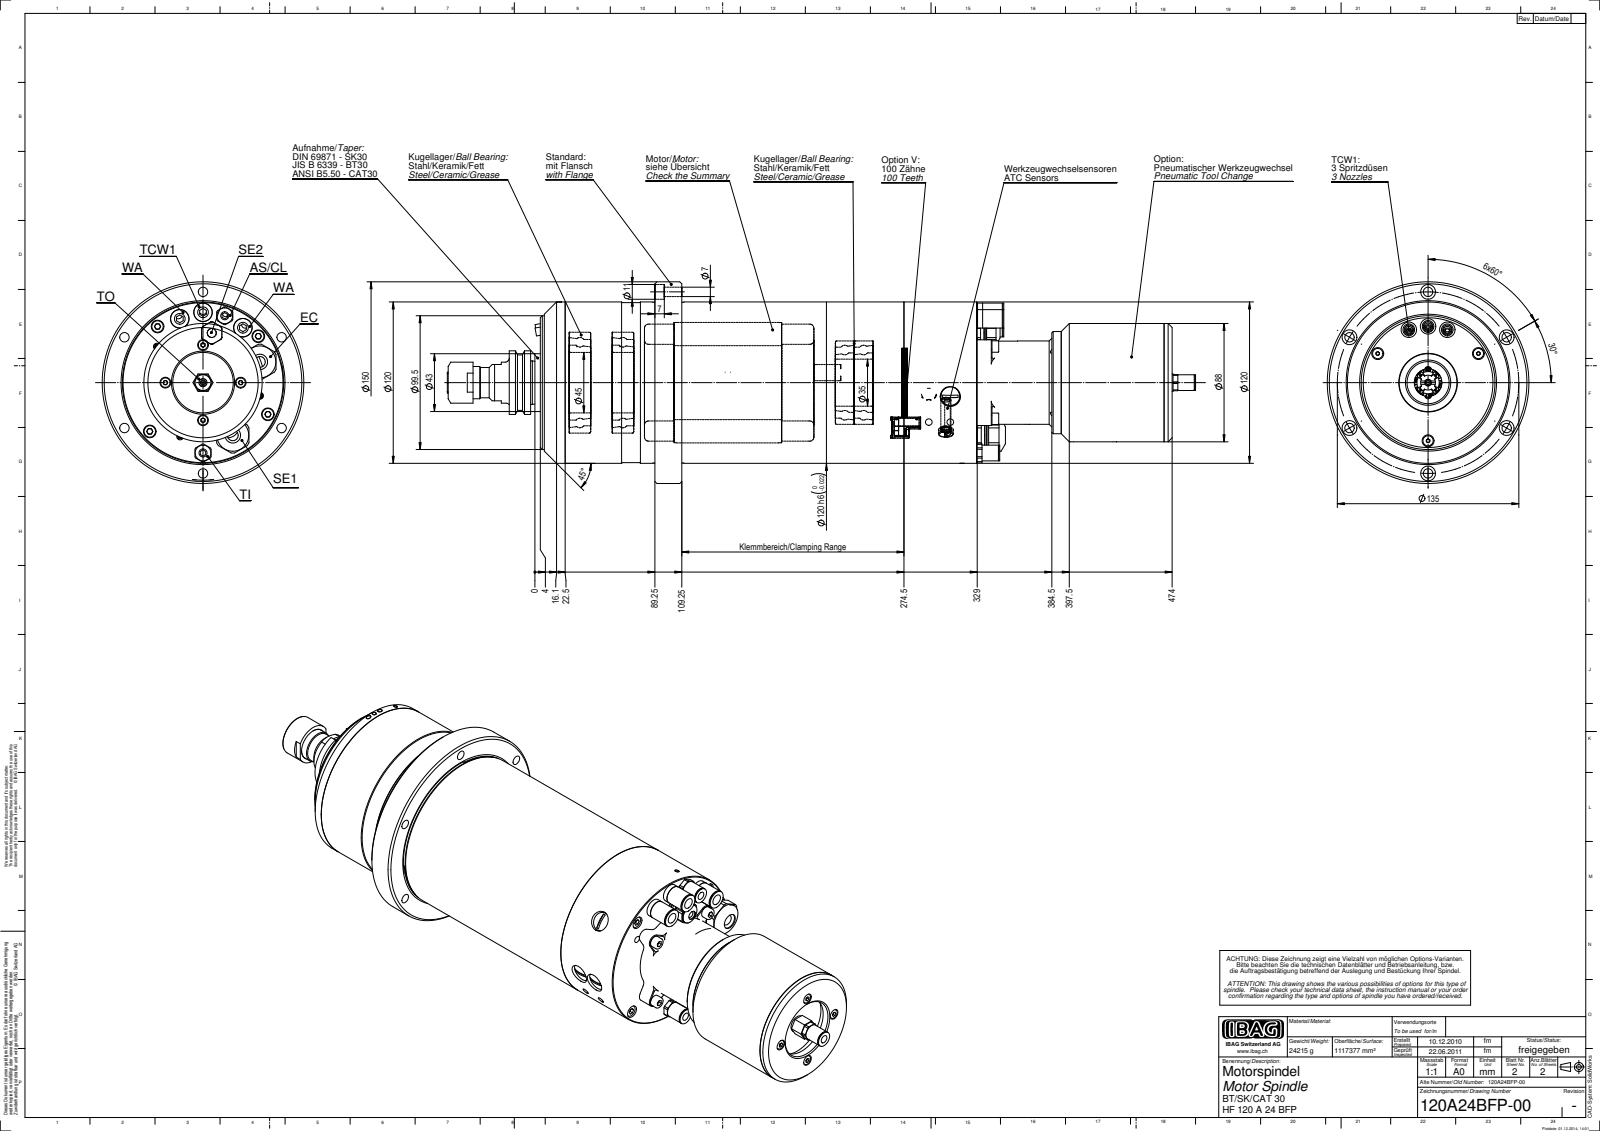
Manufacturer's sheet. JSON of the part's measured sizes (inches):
{"part_name": "120A24BFP-00", "step_written_by": "SolidWorks 2012 (CONFIG_CONTROL_DESIGN)", "units": "inches", "bodies": {"solids": 0, "faces": 818, "planar": 305, "cylindrical": 332, "other": 181}, "overall_size": [21.913, 5.906, 5.906], "round_holes": [[0.315, 9], [0.197, 6], [0.276, 6], [0.433, 6], [0.236, 5], [0.453, 5], [0.591, 5], [0.165, 4], [0.37, 4], [0.098, 3], [0.177, 3], [0.394, 3]], "round_bosses_or_shafts": [[0.335, 4], [0.276, 4], [0.539, 3], [0.461, 3], [0.301, 3], [0.236, 3], [0.933, 2], [0.878, 2]], "partial_cylinders_radius": [[0.197, 14], [0.26, 3], [0.52, 2], [0.325, 1], [0.394, 1], [0.872, 1]], "face_to_face_distances": [12.067, 12.795, 14.528, 2.461, 0.728, 17.539, 5.472, 3.012, 15.256, 18.268], "hole_center_spacings": [2.657, 4.603, 1.339, 2.114, 2.415, 4.096, 0.688, 1.408]}
